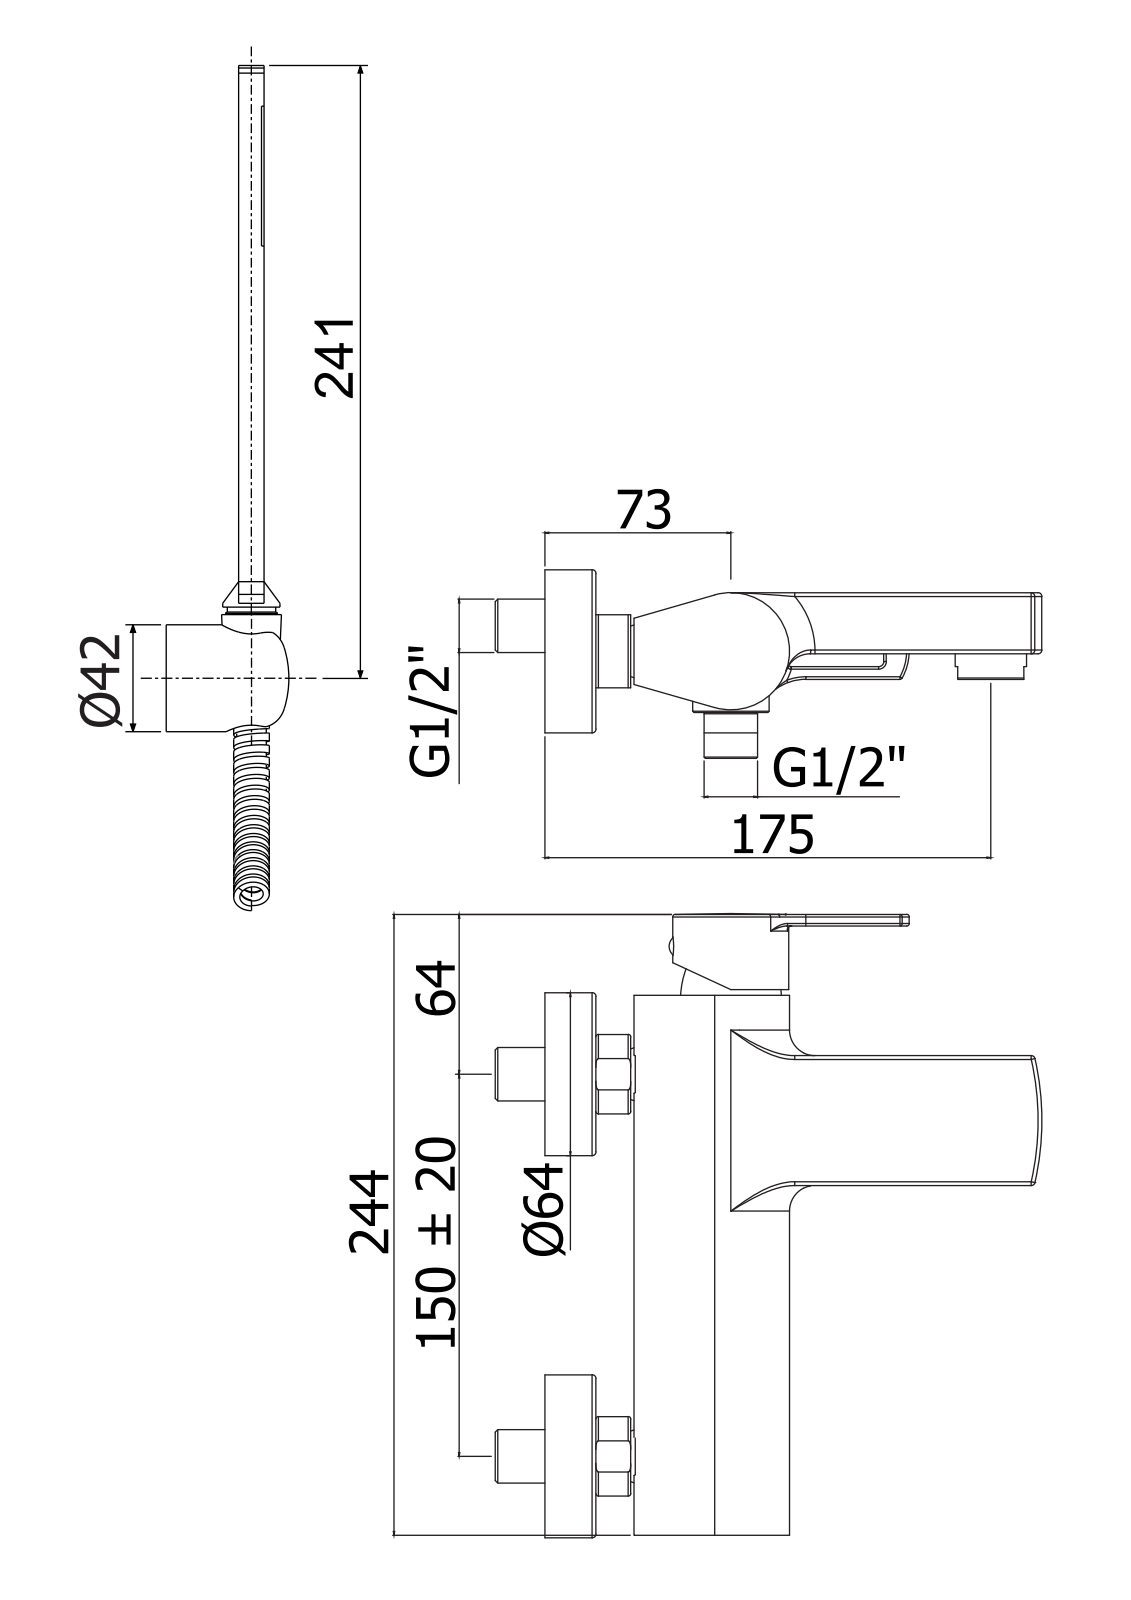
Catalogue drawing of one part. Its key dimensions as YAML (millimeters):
part_name: "RIN026CR"
step_written_by: "CREO PARAMETRIC BY PTC INC, 2020044 (CONFIG_CONTROL_DESIGN)"
units: millimeters
bodies: {solids: 3, faces: 3444, planar: 2518, cylindrical: 499, other: 427}
overall_size: [385.7, 327.75, 195]
volume: 436596
surface_area: 265042
round_holes:
  - {diameter: 7, count: 4}
  - {diameter: 5, count: 3}
  - {diameter: 20, count: 3}
  - {diameter: 4, count: 2}
  - {diameter: 8, count: 2}
  - {diameter: 9.5, count: 2}
  - {diameter: 10.5, count: 2}
  - {diameter: 12.7, count: 2}
  - {diameter: 18, count: 2}
  - {diameter: 21, count: 2}
  - {diameter: 21.6, count: 2}
  - {diameter: 28.5, count: 2}
round_bosses_or_shafts:
  - {diameter: 2, count: 11}
  - {diameter: 27, count: 3}
  - {diameter: 24, count: 3}
  - {diameter: 12, count: 3}
  - {diameter: 63.5, count: 2}
  - {diameter: 28, count: 2}
  - {diameter: 26.5, count: 2}
  - {diameter: 26.2, count: 2}
partial_cylinders:
  - {radius: 0.5, count: 34}
  - {radius: 1, count: 14}
  - {radius: 0.15, count: 11}
  - {radius: 0.3, count: 8}
  - {radius: 1.5, count: 6}
  - {radius: 6, count: 4}
  - {radius: 1.3, count: 2}
  - {radius: 2, count: 2}
face_to_face_distances: [3.5, 3, 8.5, 10, 7, 20.5, 19.5, 12.5, 12, 6.5]
hole_center_spacings: [7.07, 8.6, 9, 11.4, 150, 1.17, 4, 6]
